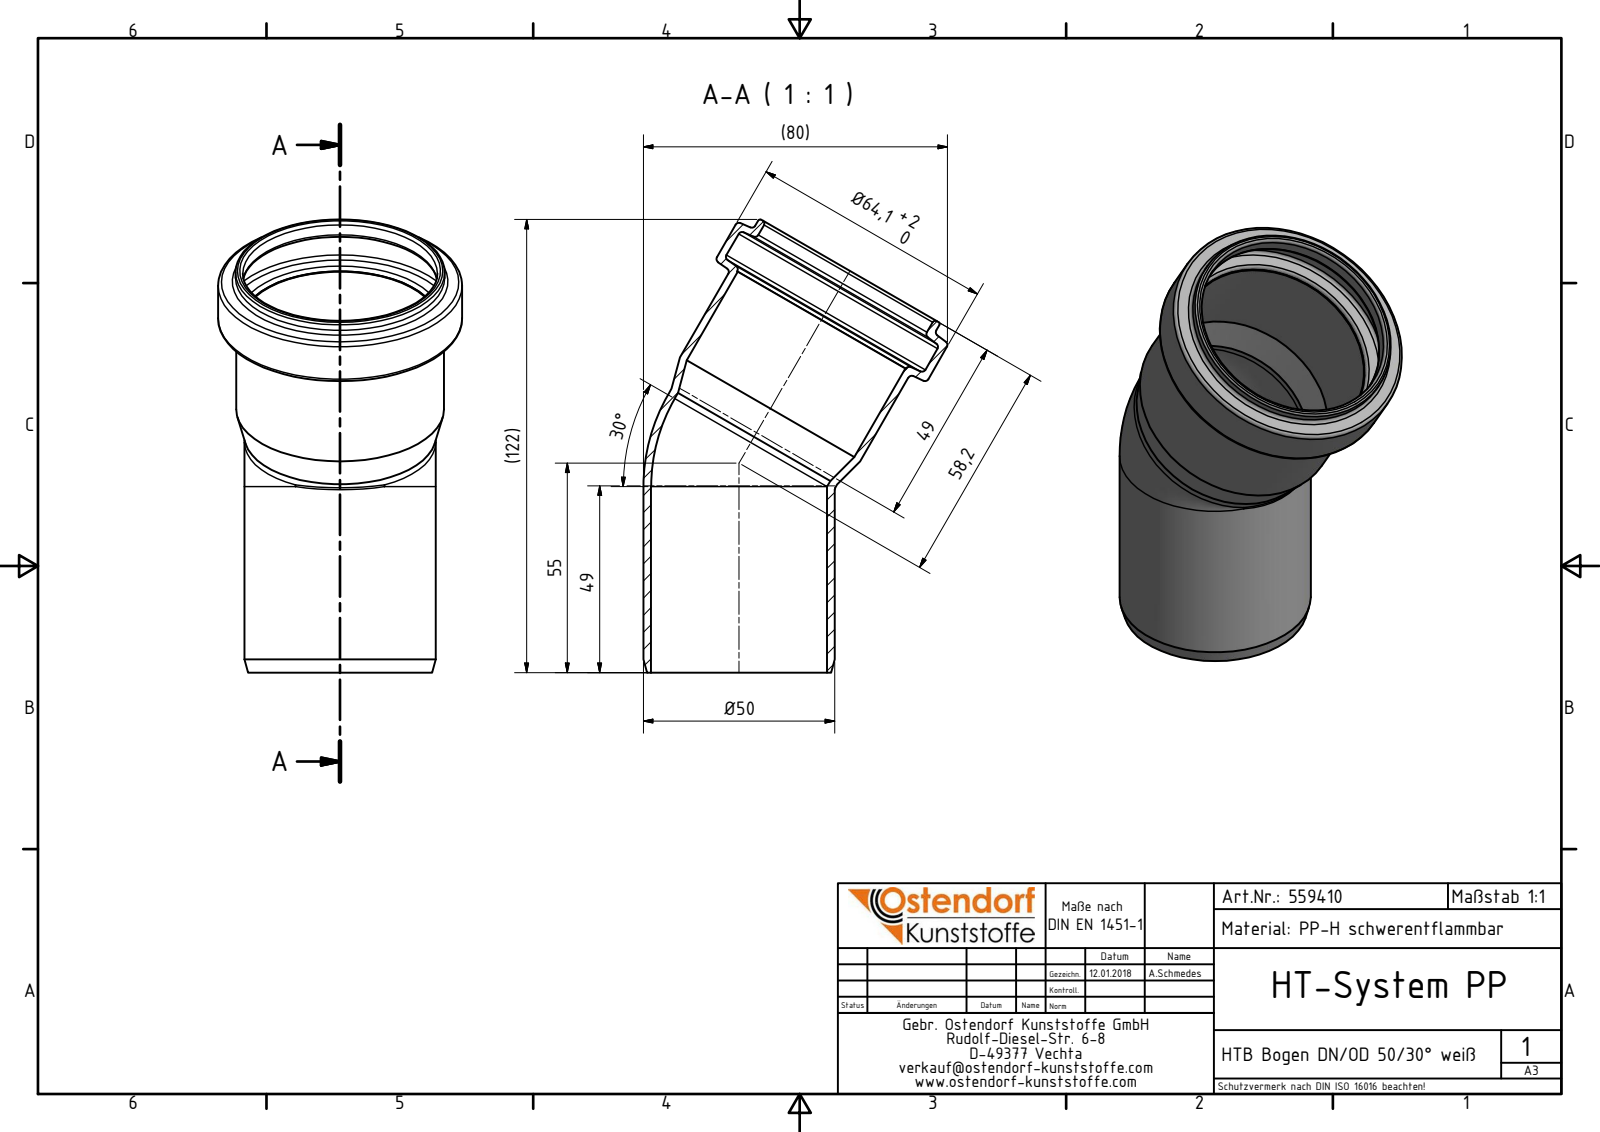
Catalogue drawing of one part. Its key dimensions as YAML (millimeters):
part_name: "559410 HTB DN_OD 50_30° weiß"
step_written_by: "Autodesk Inventor 2016 (AUTOMOTIVE_DESIGN)"
units: millimeters
bodies: {solids: 1, faces: 34, planar: 3, cylindrical: 11, other: 20}
overall_size: [118.94, 79.85, 64.1]
volume: 37599
surface_area: 39182
round_holes:
  - {diameter: 46.2, count: 2}
  - {diameter: 50.8, count: 1}
  - {diameter: 51.1, count: 1}
  - {diameter: 60.3, count: 1}
round_bosses_or_shafts:
  - {diameter: 50.2, count: 2}
  - {diameter: 64.1, count: 1}
  - {diameter: 54.9, count: 1}
  - {diameter: 54.6, count: 1}
face_to_face_distances: [14.9]
